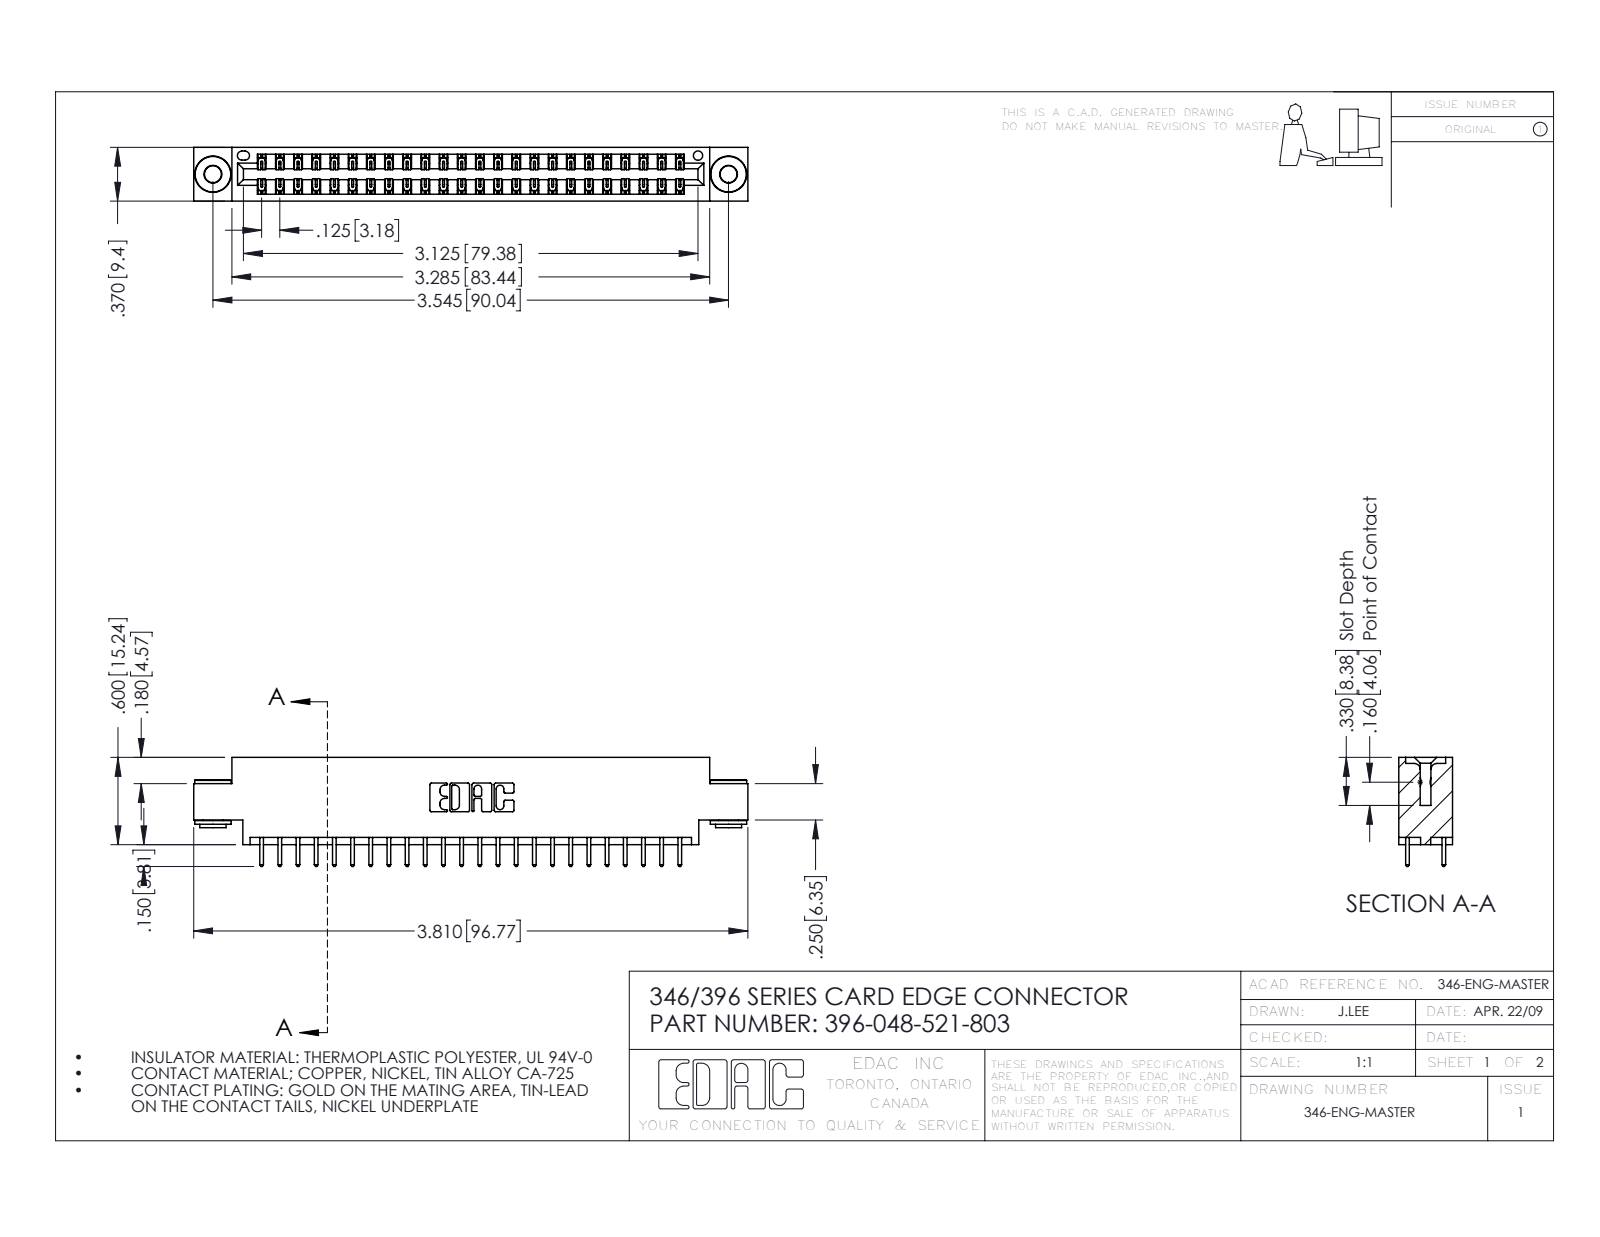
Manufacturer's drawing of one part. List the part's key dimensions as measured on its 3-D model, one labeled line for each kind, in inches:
Part name (STEP PRODUCT): 396-048-521-803; 345-292-001_345-293-121; 345-250-002_345-250-002-102; 346 Part_0.170 Offset - 0.156 Dia-TH
STEP written by: SolidWorks 2016 (CONFIG_CONTROL_DESIGN)
Units: inches
Bodies: 51 solids, 2660 faces (1770 planar, 882 cylindrical, 8 other)
Overall size (bounding box): 3.81 × 0.75 × 0.37
Volume: 0.558 in³ · Surface area: 19.45 in²
Round holes (diameter × count): ⌀0.116 ×2, ⌀0.156 ×2, ⌀0.064 ×1
Round bosses / shafts (diameter × count): ⌀0.25 ×2, ⌀0.18 ×2, ⌀0.136 ×2
Partial cylindrical surfaces — rounded edges, fillets, slot ends (radius × count): R0.006 ×72, R0.01 ×48, R0.01 ×22, R0.007 ×6, R0.031 ×6, R0.026 ×3, R0.014 ×2, R0.022 ×2
Main face-to-face distances: 0.048, 0.322, 0.37, 0.25, 0.025, 0.072, 0.298, 0.275, 0.148, 0.222
Hole centre spacings: 0.246, 3.337, 3.545
